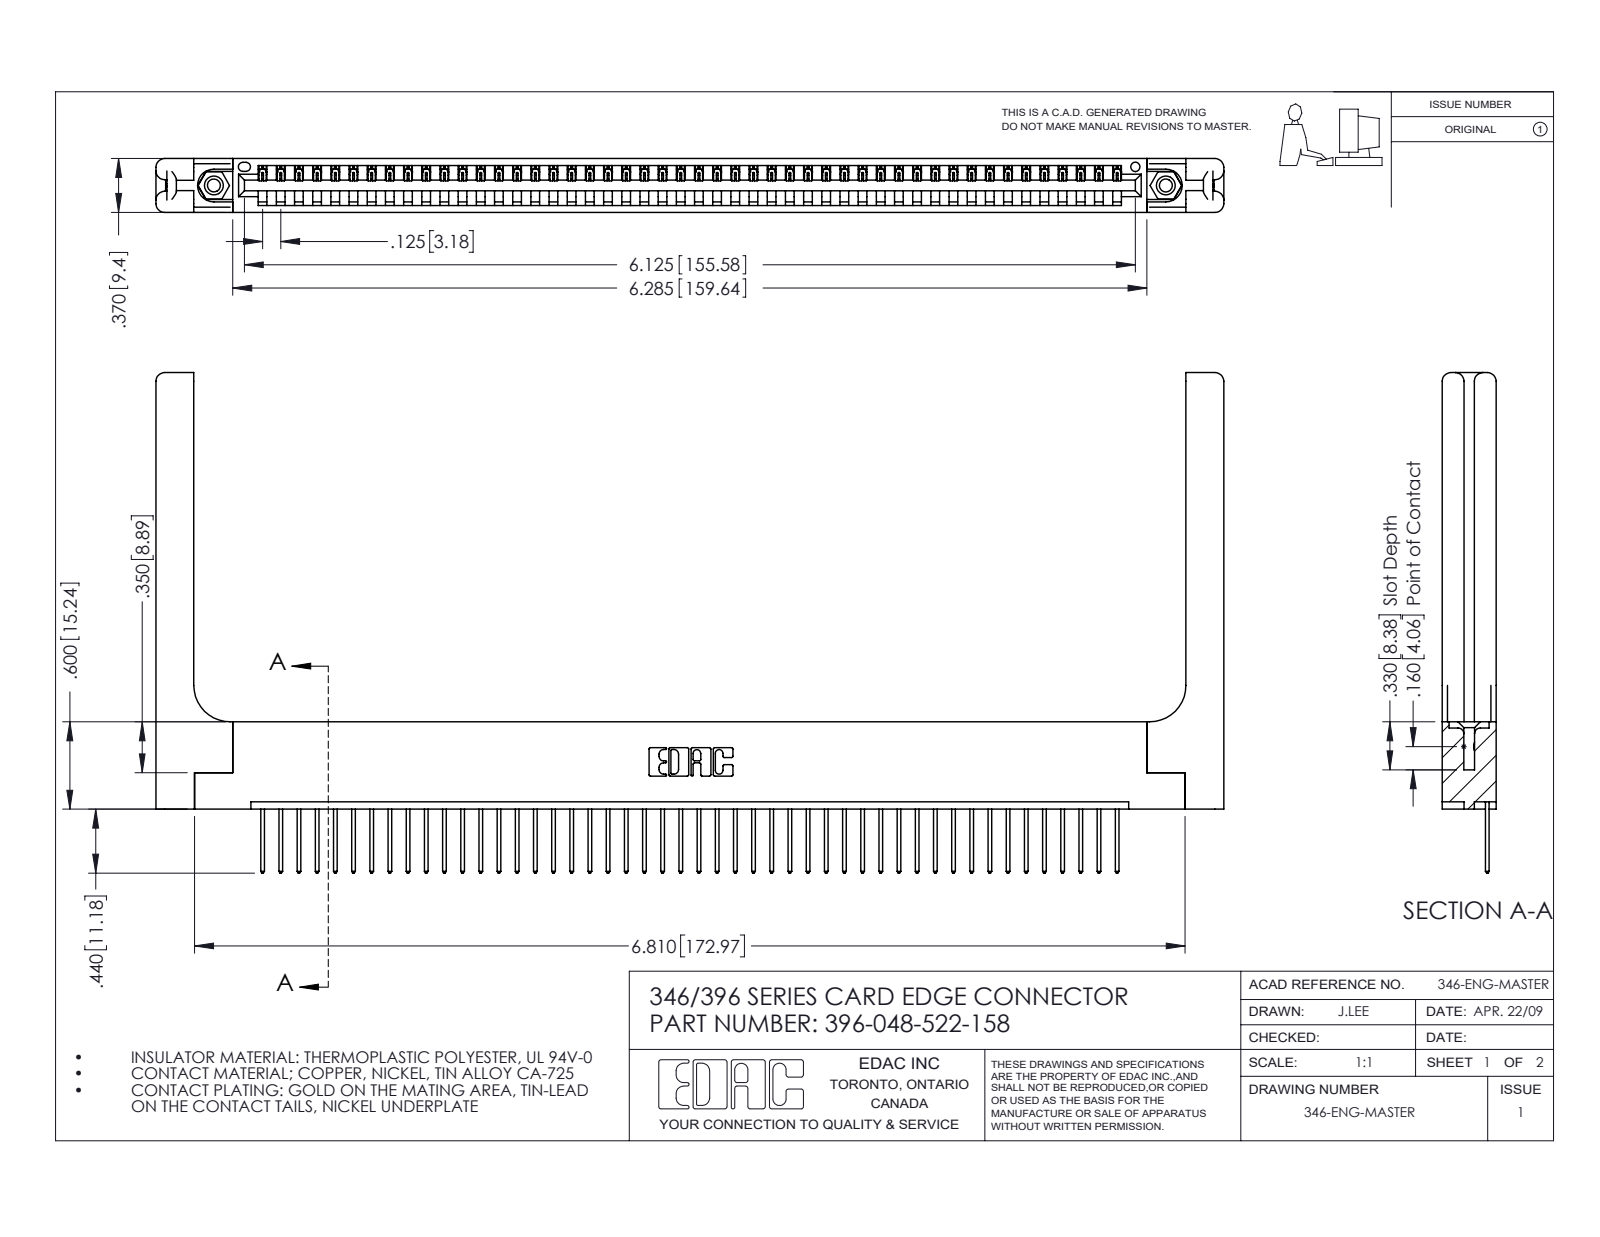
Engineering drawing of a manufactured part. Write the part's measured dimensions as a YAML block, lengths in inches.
part_name: "346 Part_Flush Mounting Lugs - 0.156 Dia-TH; 346-220-058_345-220-058; 345-250-001_345-250-001-102; 345-292-001_345-293-122 (+1 more)"
step_written_by: "SolidWorks 2016 (CONFIG_CONTROL_DESIGN)"
units: inches
bodies: {solids: 53, faces: 3162, planar: 2144, cylindrical: 958, other: 60}
overall_size: [7.341, 3.44, 0.37]
volume: 1.551
surface_area: 43.06
round_holes:
  - {diameter: 0.089, count: 2}
  - {diameter: 0.125, count: 2}
  - {diameter: 0.156, count: 2}
  - {diameter: 0.064, count: 1}
round_bosses_or_shafts:
  - {diameter: 0.155, count: 2}
partial_cylinders:
  - {radius: 0.006, count: 96}
  - {radius: 0.01, count: 96}
  - {radius: 0.01, count: 22}
  - {radius: 0.06, count: 16}
  - {radius: 0.007, count: 6}
  - {radius: 0.031, count: 6}
  - {radius: 0.026, count: 3}
  - {radius: 0.03, count: 2}
face_to_face_distances: [0.37, 0.048, 0.322, 0.072, 0.148, 0.15, 0.25, 0.298, 0.025, 0.222]
hole_center_spacings: [0.246, 6.336, 6.545]
